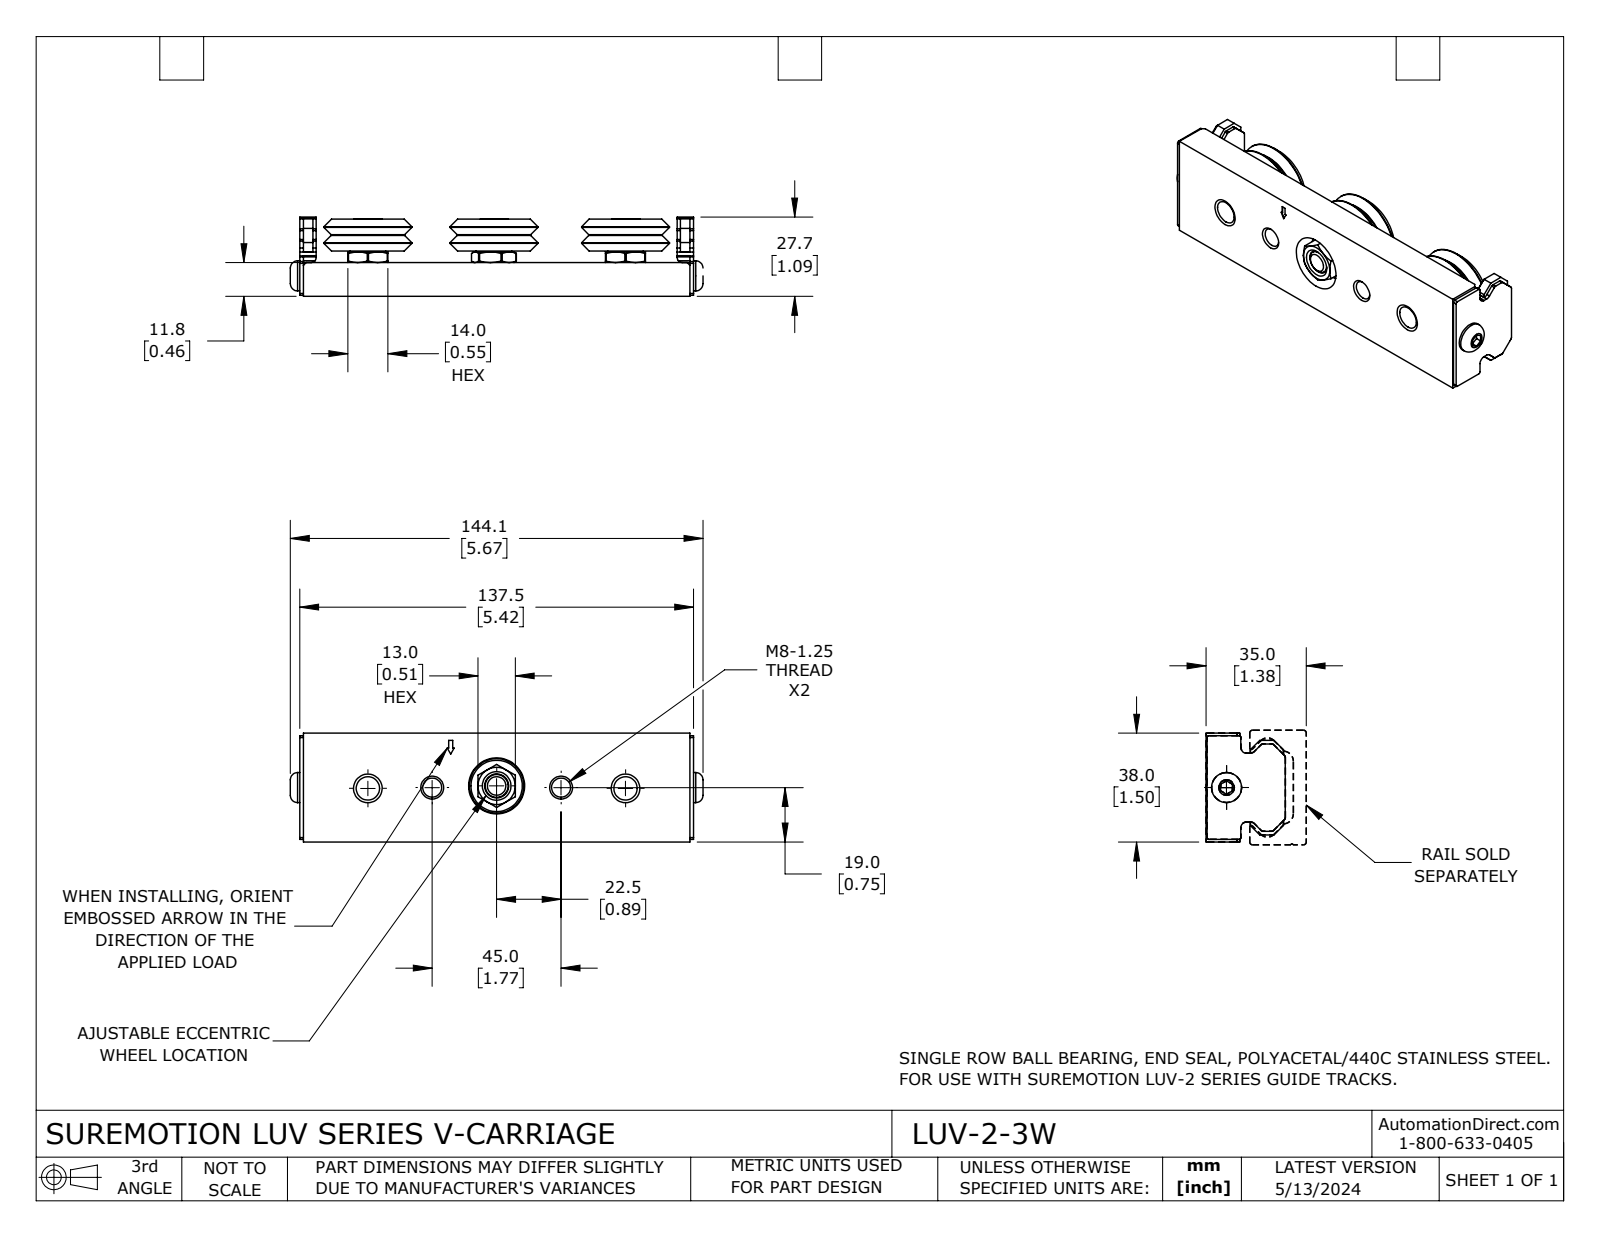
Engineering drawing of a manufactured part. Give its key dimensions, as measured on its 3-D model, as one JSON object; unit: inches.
{"part_name": "LUV-2-3W", "step_written_by": "SolidWorks 2023 (CONFIG_CONTROL_DESIGN)", "units": "inches", "bodies": {"solids": 7, "faces": 678, "planar": 236, "cylindrical": 200, "other": 242}, "overall_size": [5.675, 1.496, 1.09], "volume_in3": 5.333, "surface_area_in2": 51.63, "round_holes": [[0.33, 3], [0.792, 3], [0.801, 3], [0.262, 2], [0.375, 2], [0.194, 1], [0.375, 1], [0.378, 1], [0.77, 1]], "round_bosses_or_shafts": [[1.21, 3], [0.584, 3], [0.575, 3], [0.374, 3], [0.394, 2], [0.303, 2], [0.705, 1], [0.413, 1]], "partial_cylinders_radius": [[0.025, 12], [0.015, 6], [0.033, 6], [0.078, 4], [0.313, 3], [0.07, 2]], "face_to_face_distances": [0.464, 1.496, 0.05, 5.365, 0.428, 5.315, 0.598, 1.062, 5.415, 0.225], "hole_center_spacings": [0.886, 0.038, 0.849, 0.885, 0.887, 0.923, 1.734, 1.772]}
